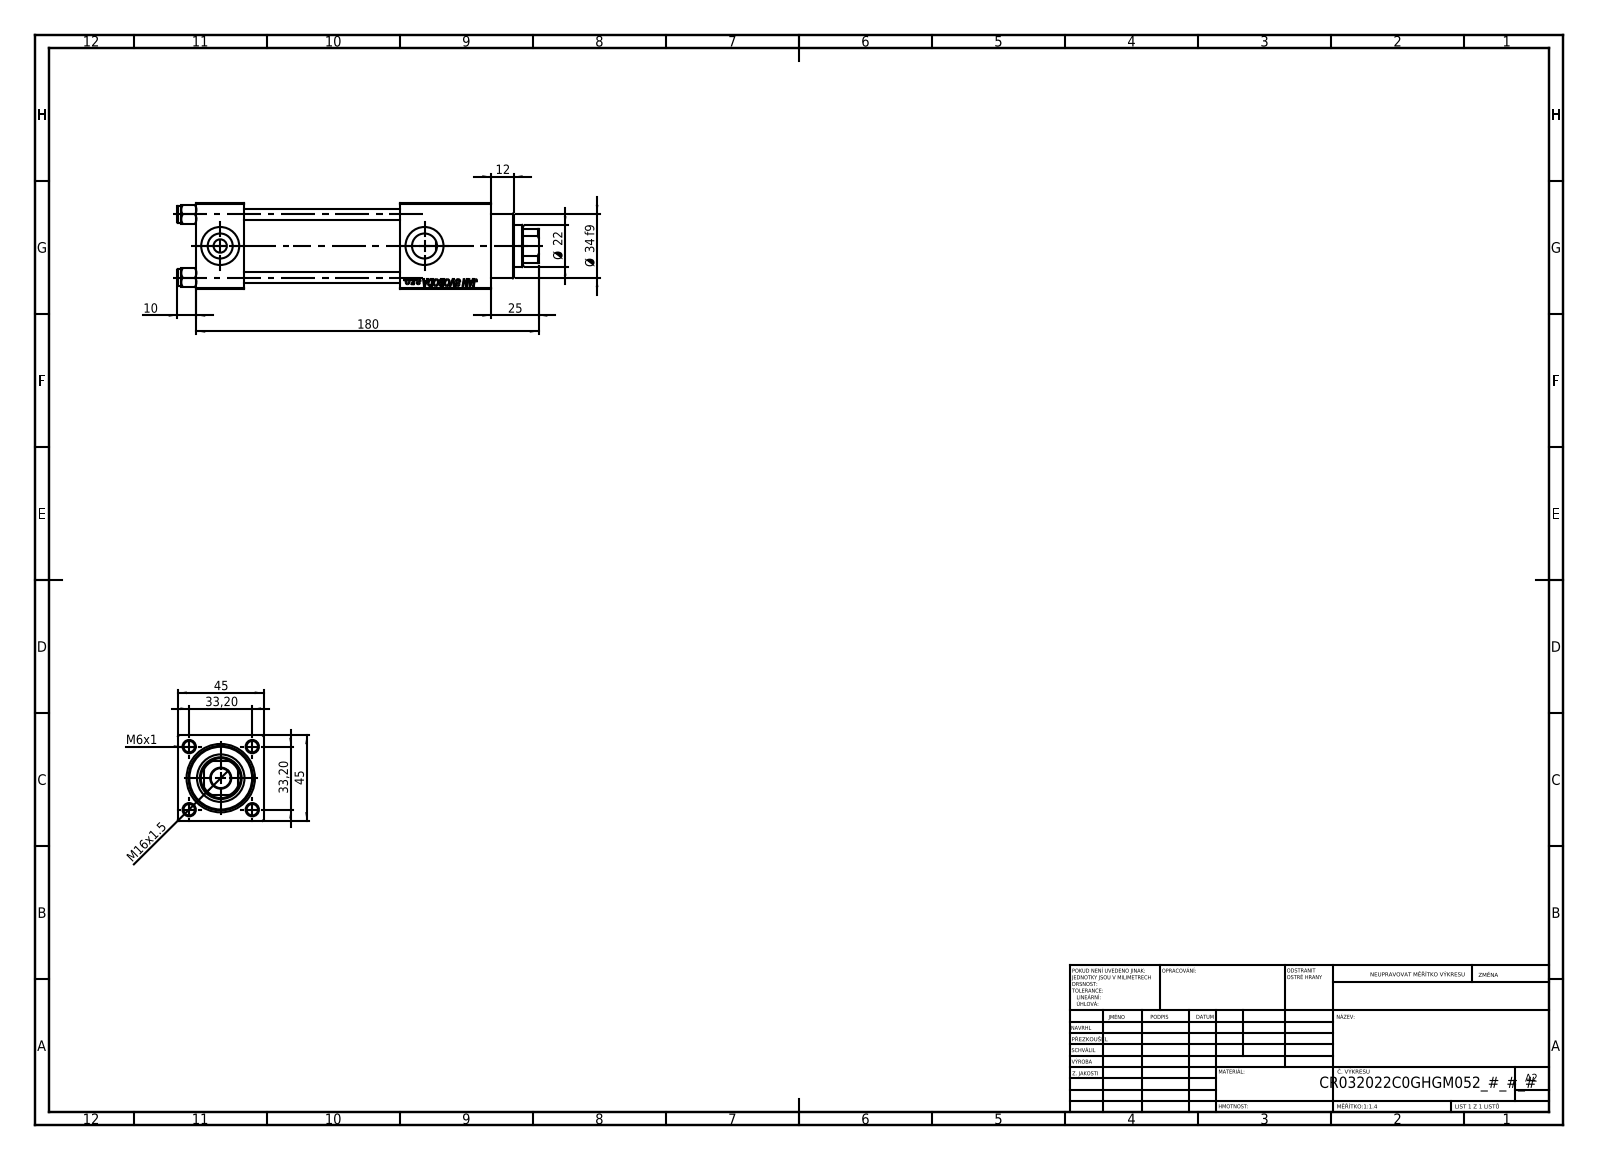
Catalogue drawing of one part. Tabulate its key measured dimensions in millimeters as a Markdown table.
| quantity | value |
| --- | --- |
| part name | V215CR_C_TYCINKA; NUT_M5_C; V215CR_C_Body; V215_VC_A (+1 more) |
| STEP written by | SolidWorks 2019 (CONFIG_CONTROL_DESIGN) |
| units | millimeters |
| bodies | 11 solids, 1147 faces (525 planar, 86 cylindrical, 536 other) |
| overall size | 190 × 45 × 45 |
| volume | 236 198 mm³ |
| surface area | 82 964 mm² |
| round holes (diameter × count) | 6 × 4, 7 × 2, 13.16 × 2, 20 × 2, 10.5 × 1, 22 × 1, 24 × 1, 25 × 1, 32 × 1, 33 × 1 |
| round bosses / shafts (diameter × count) | 9 × 4, 38 × 1, 34 × 1 |
| partial cylindrical surfaces (radius × count) | 10.5 × 1 |
| main face-to-face distances | 45, 25, 155, 107, 82, 130, 48, 126.3, 101.3, 19.3 |
| hole center spacings | 23.48, 33.2, 46.95, 107.5 |
